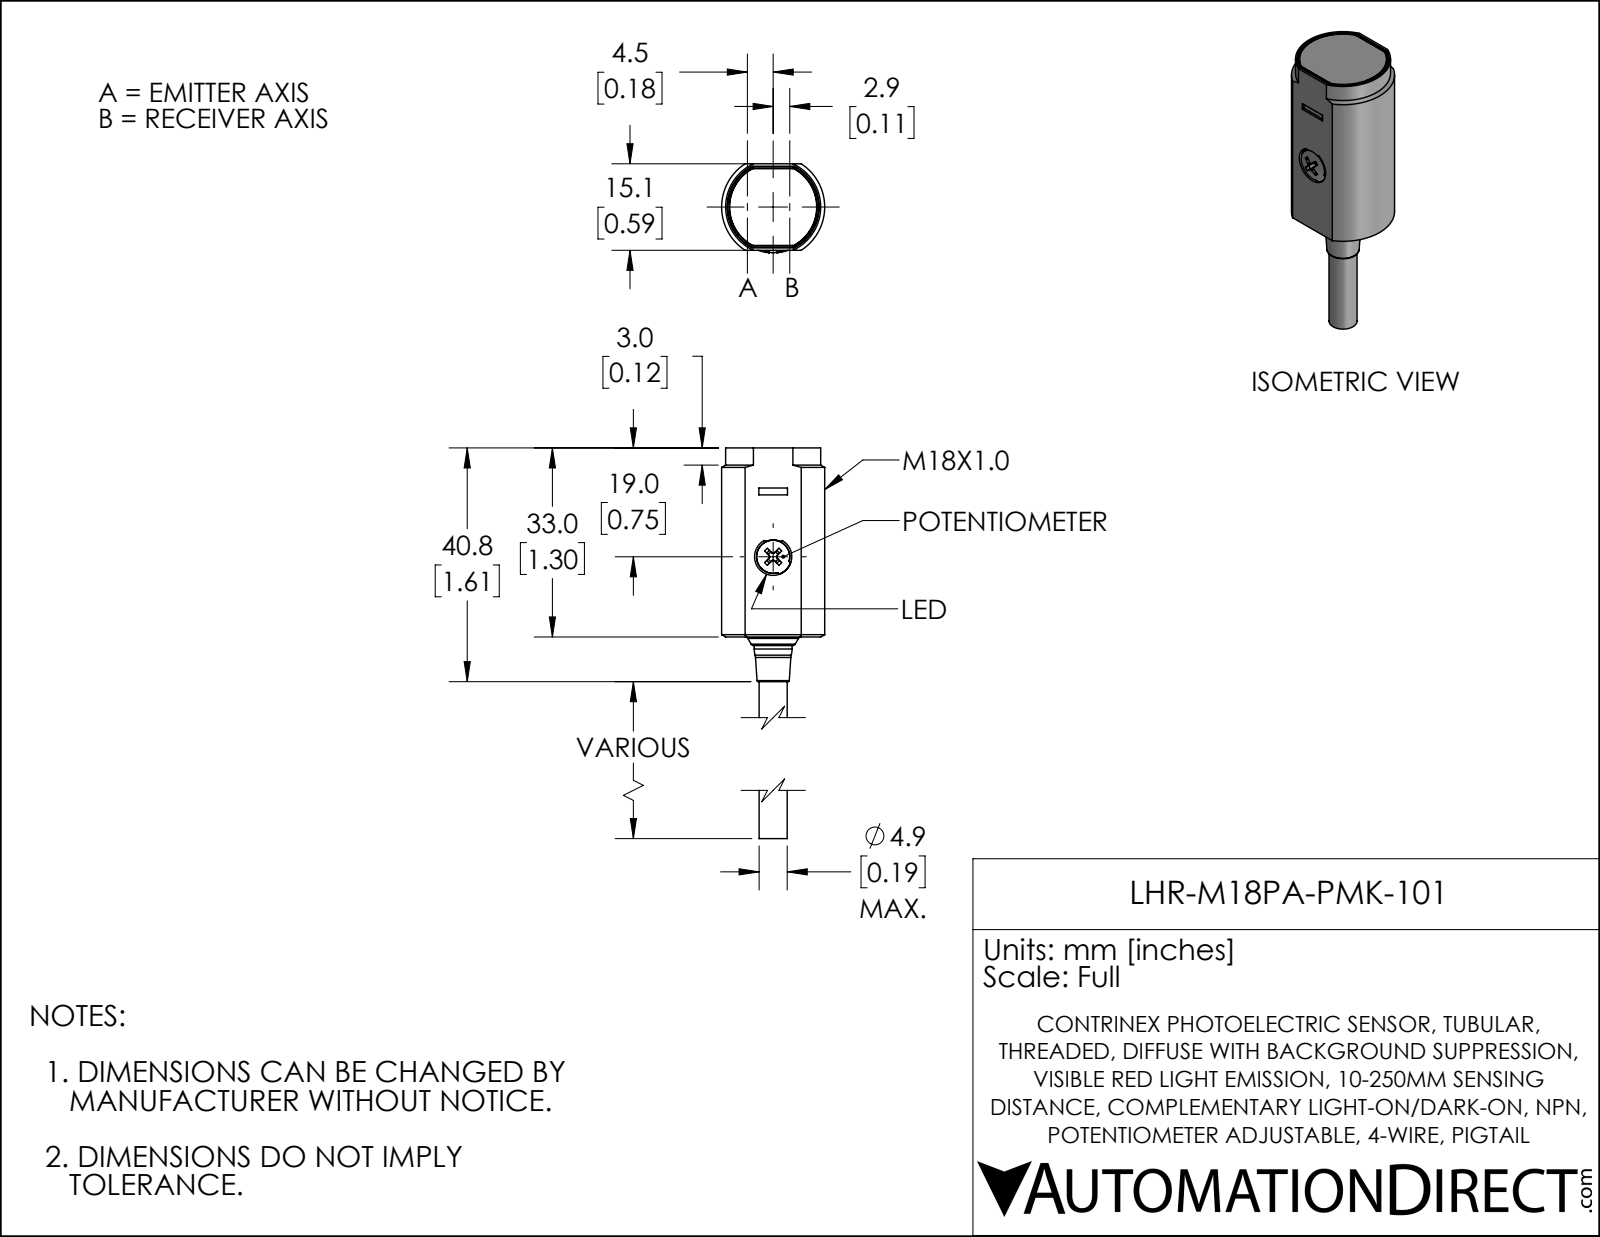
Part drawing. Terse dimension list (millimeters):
name: LHR-M18PA-PMK-101
written by: SolidWorks 2021 (AUTOMOTIVE_DESIGN)
unit: mm
bodies: 1 solid, 116 faces (58 planar, 40 cylindrical, 18 other)
size: 56 × 18 × 15.5
volume: 8 190 mm³; area: 2 750 mm²
holes: 1× ⌀6.5
bosses: 1× ⌀6.6, 1× ⌀4.9
rounds: 8× R0.4, 8× R0.7, 4× R0.2, 4× R0.6, 1× R2.9, 1× R7.6, 1× R7.7, 1× R8
face distances: 15.1, 32.9, 0.4, 33, 56, 56, 23, 14.7, 14.3, 0.4
